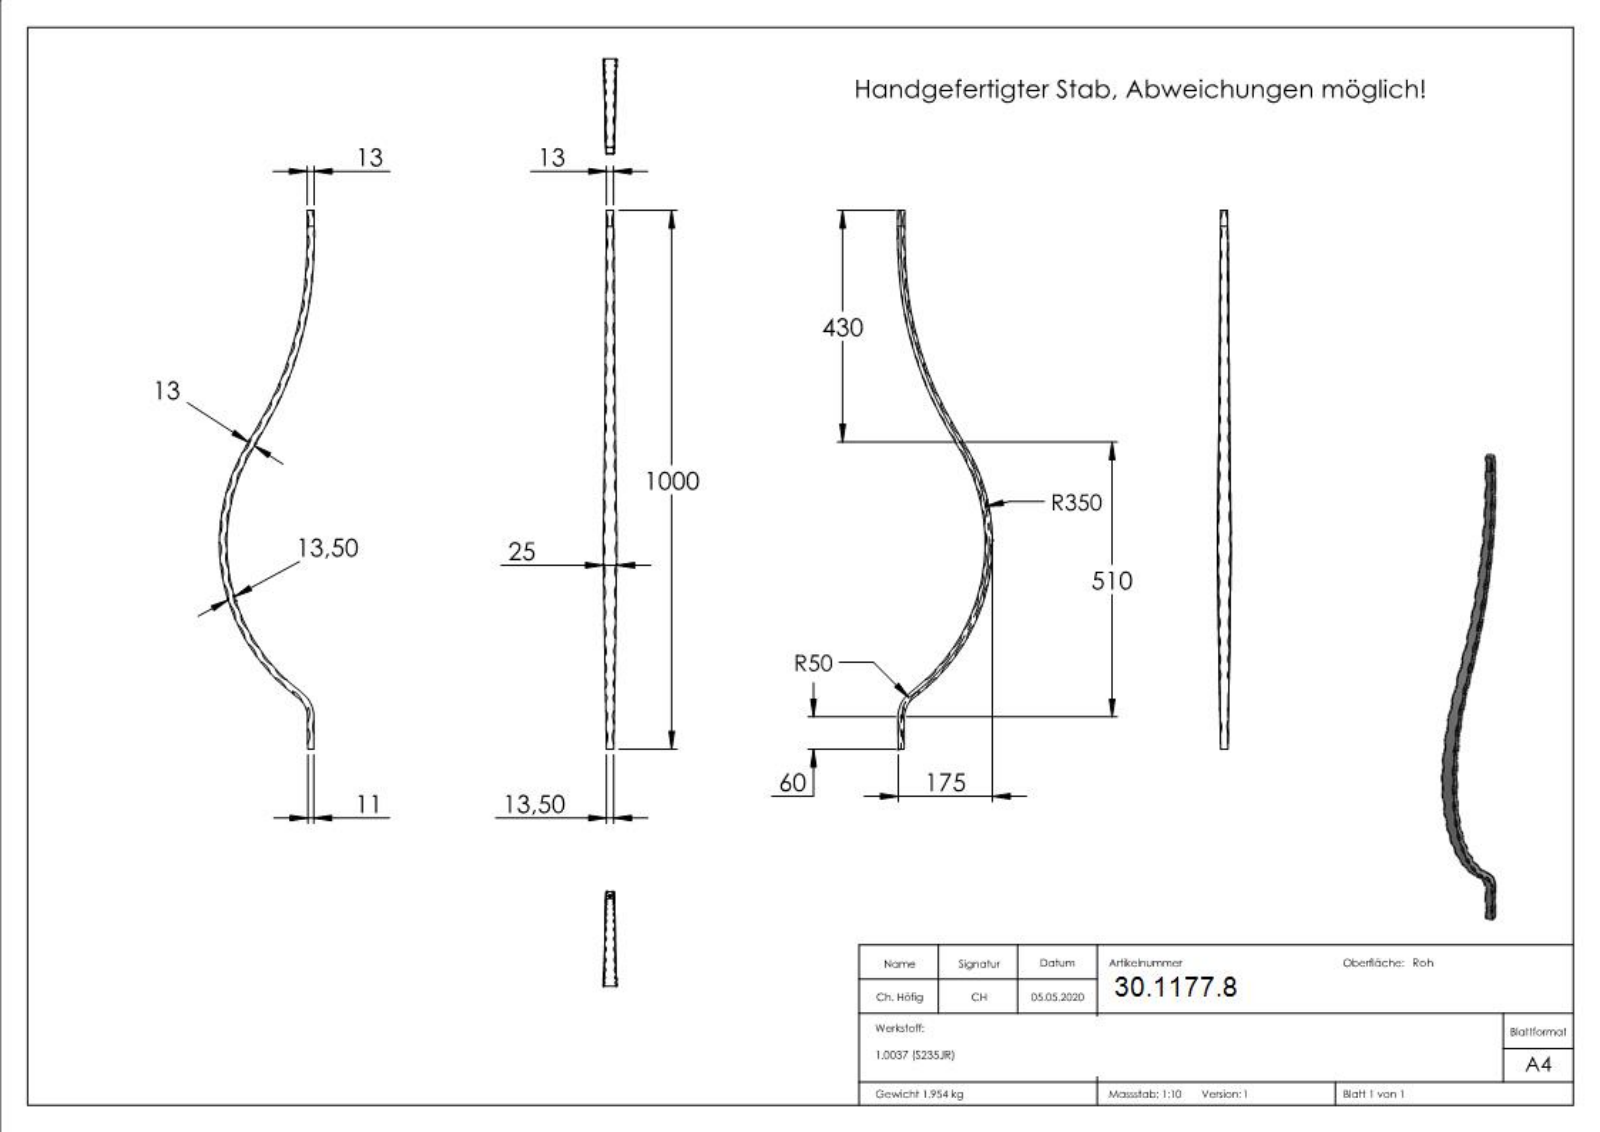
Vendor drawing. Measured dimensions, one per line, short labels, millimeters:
name: 1746
written by: SolidWorks 2015 (CONFIG_CONTROL_DESIGN)
unit: mm
bodies: 1 solid, 270 faces (105 planar, 0 cylindrical, 165 other)
size: 1000 × 176.33 × 25
volume: 5 322 000 mm³; area: 100 288 mm²
face distances: 13, 1000, 999.9, 0.55, 1.71, 0.46, 2.23, 0.31, 2.26, 2.93
